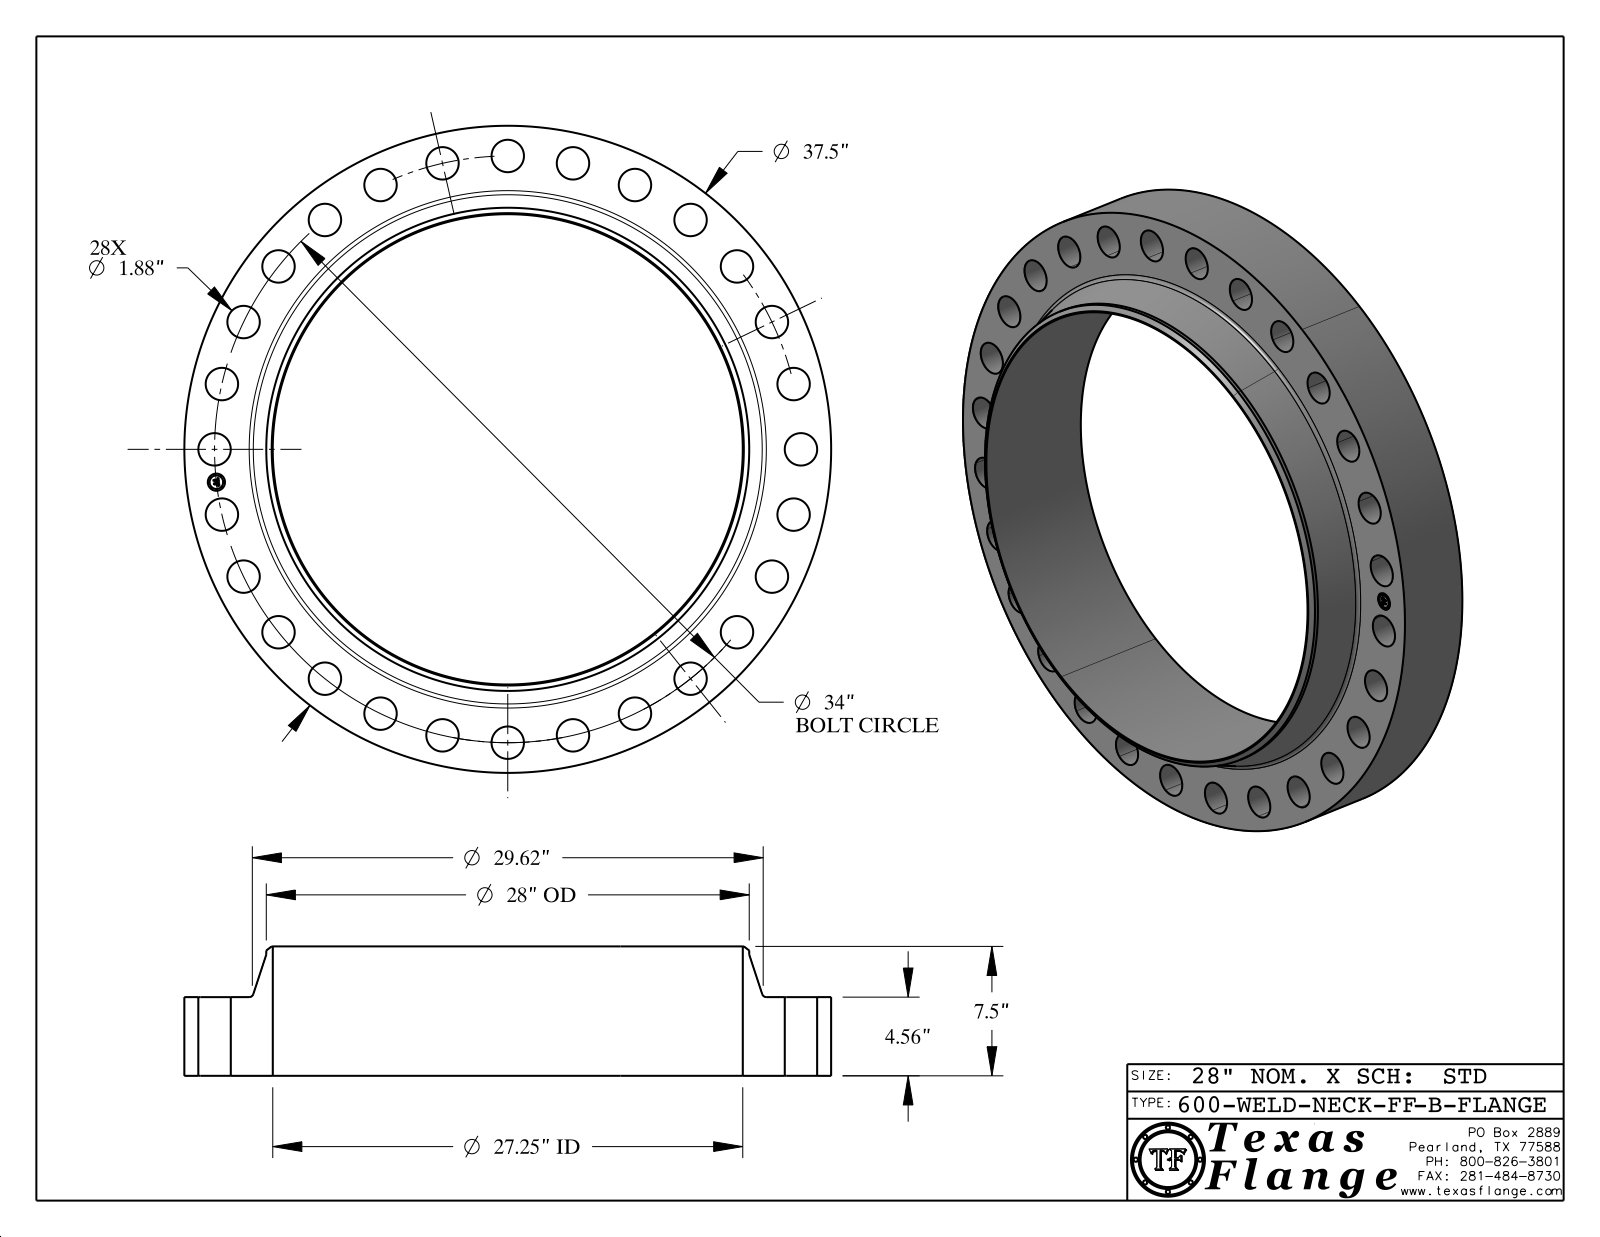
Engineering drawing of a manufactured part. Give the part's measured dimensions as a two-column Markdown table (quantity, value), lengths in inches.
| quantity | value |
| --- | --- |
| part name | 600-WELD-NECK-FF, Series B |
| STEP written by | CATIA V5 STEP AP214 (AUTOMOTIVE_DESIGN) |
| units | inches |
| bodies | 1 solid, 456 faces (368 planar, 82 cylindrical, 6 other) |
| overall size | 37.5 × 37.5 × 7.5 |
| volume | 2 205 in³ |
| surface area | 3 005 in² |
| round holes (diameter × count) | 1.88 × 28, 1 × 1, 27.25 × 1 |
| round bosses / shafts (diameter × count) | 0.061 × 8, 37.5 × 1, 28 × 1, 0.788 × 1 |
| main face-to-face distances | 4.56, 7.5, 2.94, 0.015, 4.545, 2.955, 0.298, 0.293, 0.054, 0.193 |
| hole center spacings | 3.807, 7.566, 30.633, 33.786, 17, 11.23, 18.089, 21.198 |
